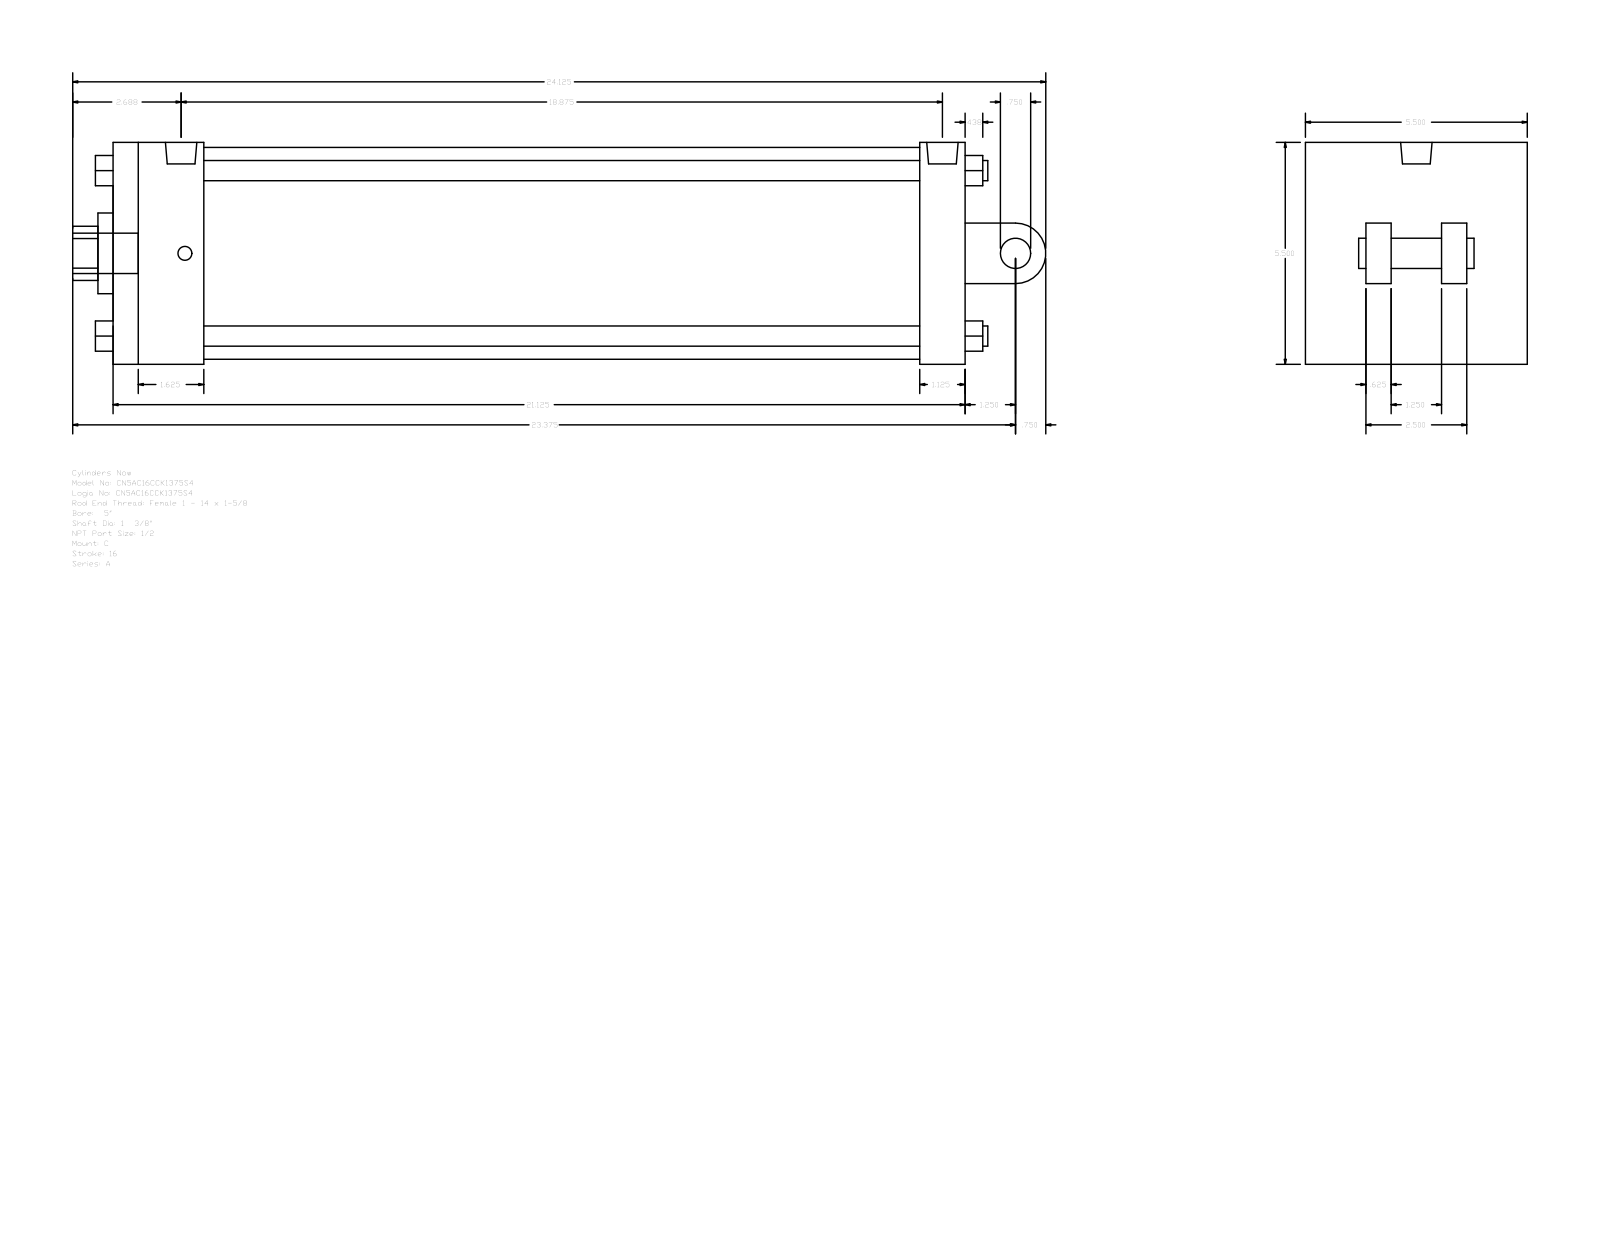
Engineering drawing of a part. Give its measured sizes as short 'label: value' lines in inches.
name: A_C__0500_1.375
written by: GSSL Pune (CONFIG_CONTROL_DESIGN)
unit: in
bodies: 0 solids, 135 faces (102 planar, 33 cylindrical, 0 other)
size: 24.125 × 5.5 × 5.5
holes: 2× ⌀0.344, 1× ⌀0.778, 1× ⌀1.375, 1× ⌀2, 1× ⌀5.25
bosses: 4× ⌀0.5, 2× ⌀0.344, 1× ⌀1, 1× ⌀0.778, 1× ⌀0.75
rounds: 1× R0.672, 1× R0.75
face distances: 5.5, 21.125, 1.125, 2.25, 20, 17.75, 18.875, 1.5, 0.625, 2.125
hole spacings: 0.094
